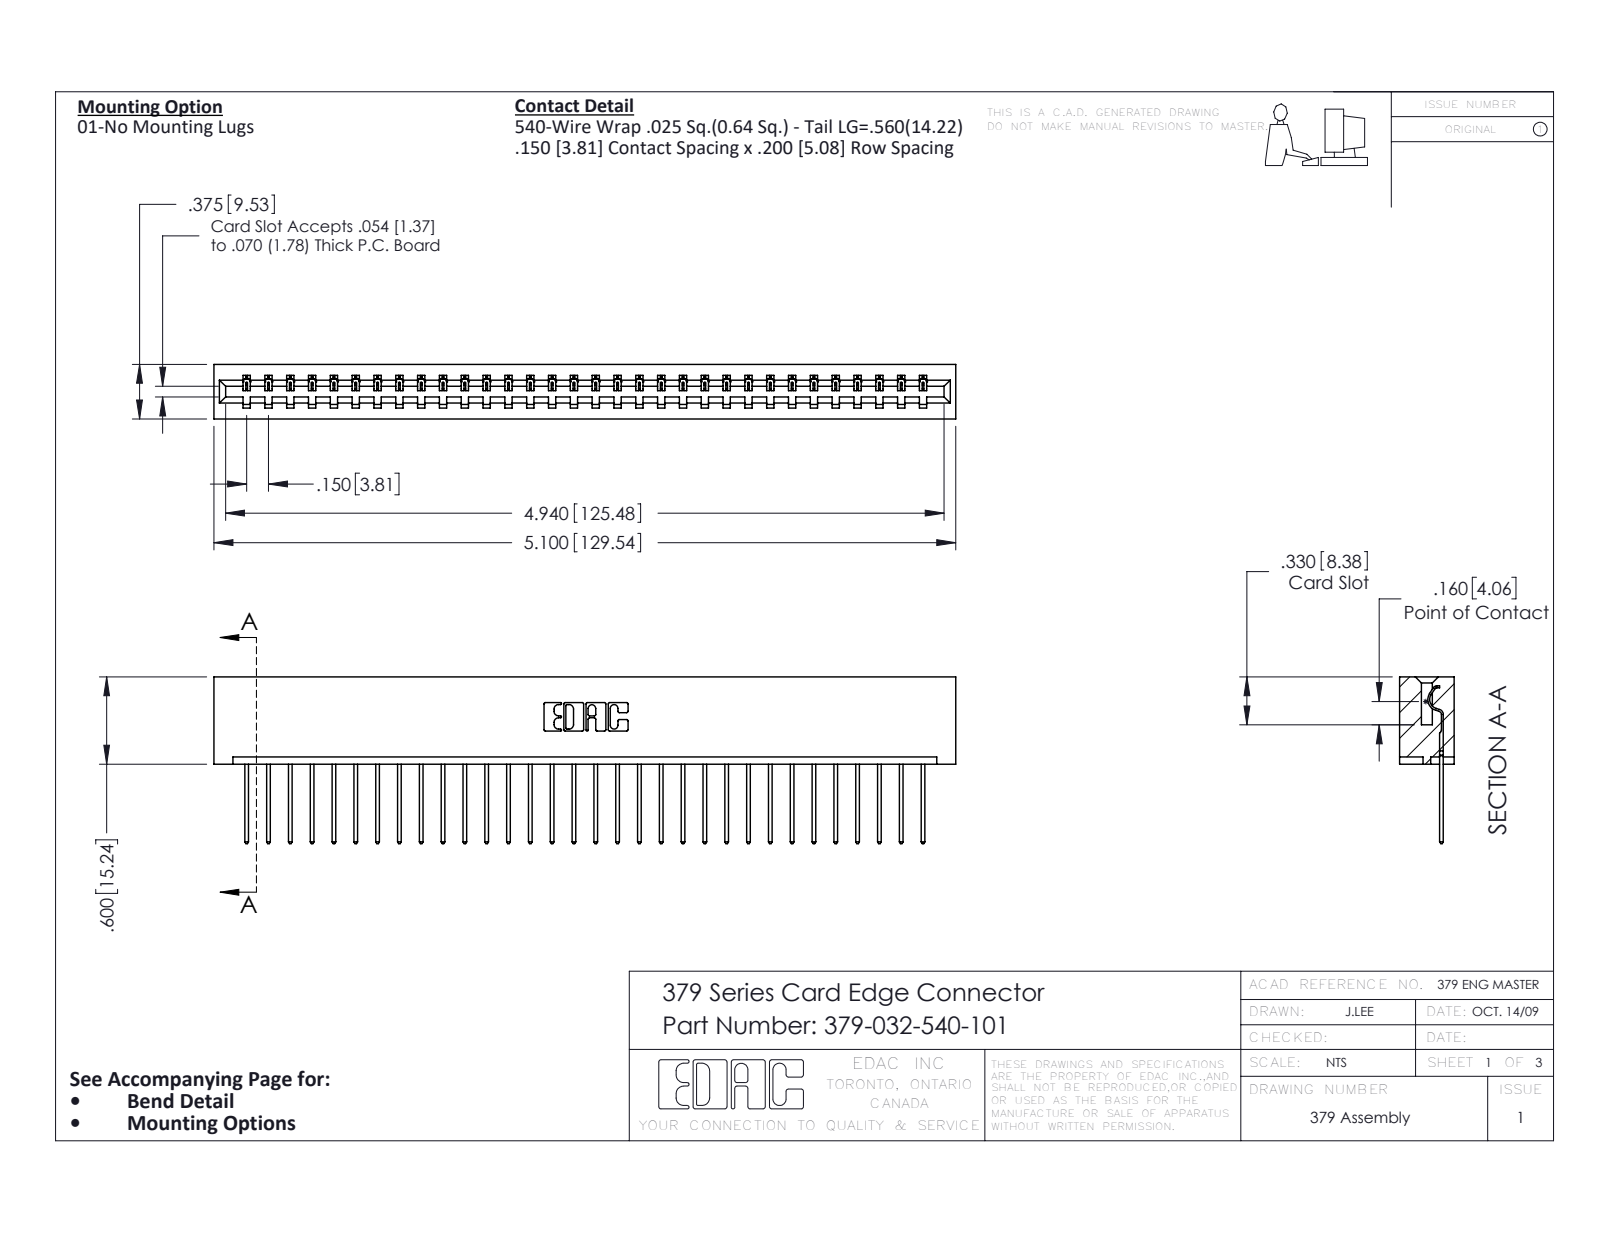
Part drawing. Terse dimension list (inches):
name: 379-032-540-101; 345-292-001_345-293-140; 379 Part_Lugless
written by: SolidWorks 2016 (CONFIG_CONTROL_DESIGN)
unit: in
bodies: 33 solids, 1962 faces (1410 planar, 552 cylindrical, 0 other)
size: 5.1 × 1.147 × 0.375
volume: 0.87 in³; area: 22.97 in²
rounds: 64× R0.006, 64× R0.01, 22× R0.01, 6× R0.007, 6× R0.031, 3× R0.026, 1× R0.014, 1× R0.022
face distances: 0.3, 0.075, 0.375, 0.225, 0.1, 0.275, 0.025, 0.6, 0.2, 0.15
